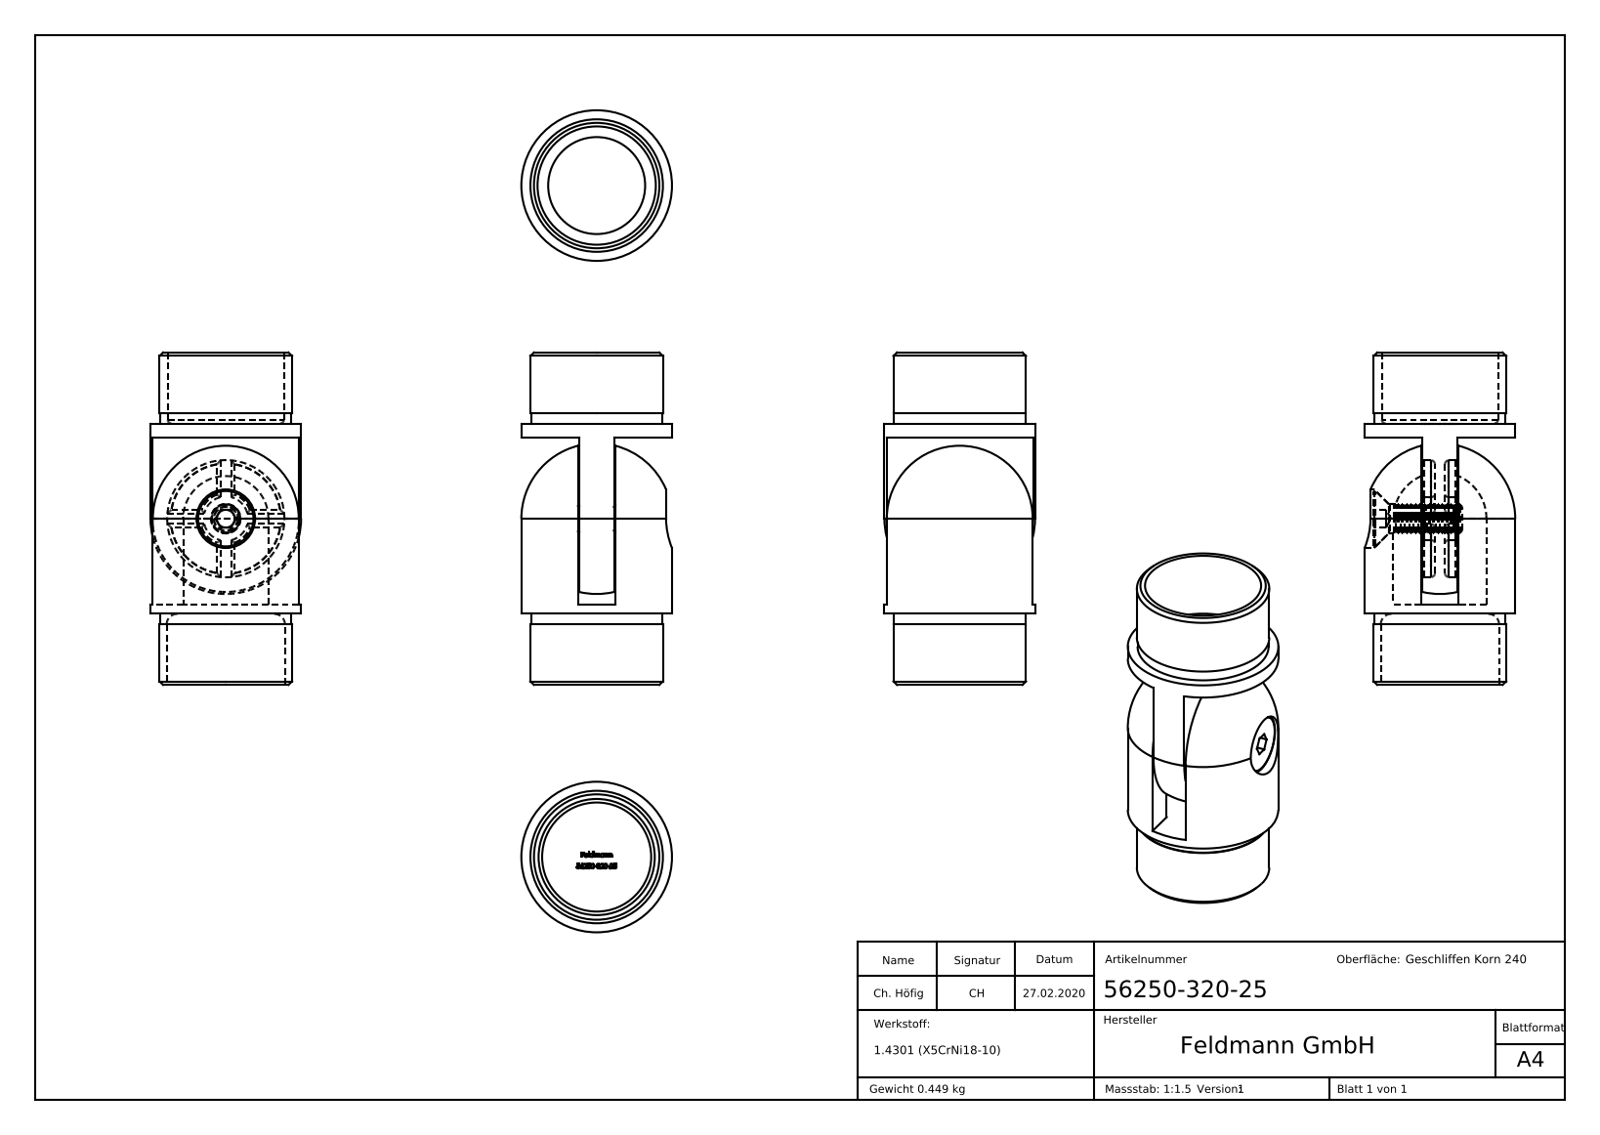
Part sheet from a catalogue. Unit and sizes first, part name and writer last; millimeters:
Units: millimetres
Overall size (bounding box): 93.6 × 42.4 × 42.4
Round holes (diameter × count): ⌀6.8 ×1, ⌀8.2 ×1, ⌀16.5 ×1, ⌀32.7 ×1, ⌀33 ×1, ⌀33.3 ×1
Round bosses / shafts (diameter × count): ⌀42.4 ×1, ⌀37.3 ×1, ⌀36.9 ×1, ⌀15.57 ×1, ⌀8 ×1
Partial cylindrical surfaces — rounded edges, fillets, slot ends (radius × count): R1 ×8, R6.25 ×1, R13.1 ×1
Main face-to-face distances: 0.35, 10.15, 4, 49.6, 53.6, 10.5, 3.5, 3.85, 6.65, 6.3
Volume: 58 068 mm³ · Surface area: 29 569 mm²
Bodies: 3 solids, 436 faces (187 planar, 56 cylindrical, 193 other)
Part name (STEP PRODUCT): 5625X-320 Teil1_56250-320-25 Teil1; socket countersunk head screw_din; 5625X-320 Teil1; 5625X-320 Teil2 (+3 more)
STEP written by: SolidWorks 2015 (CONFIG_CONTROL_DESIGN)
